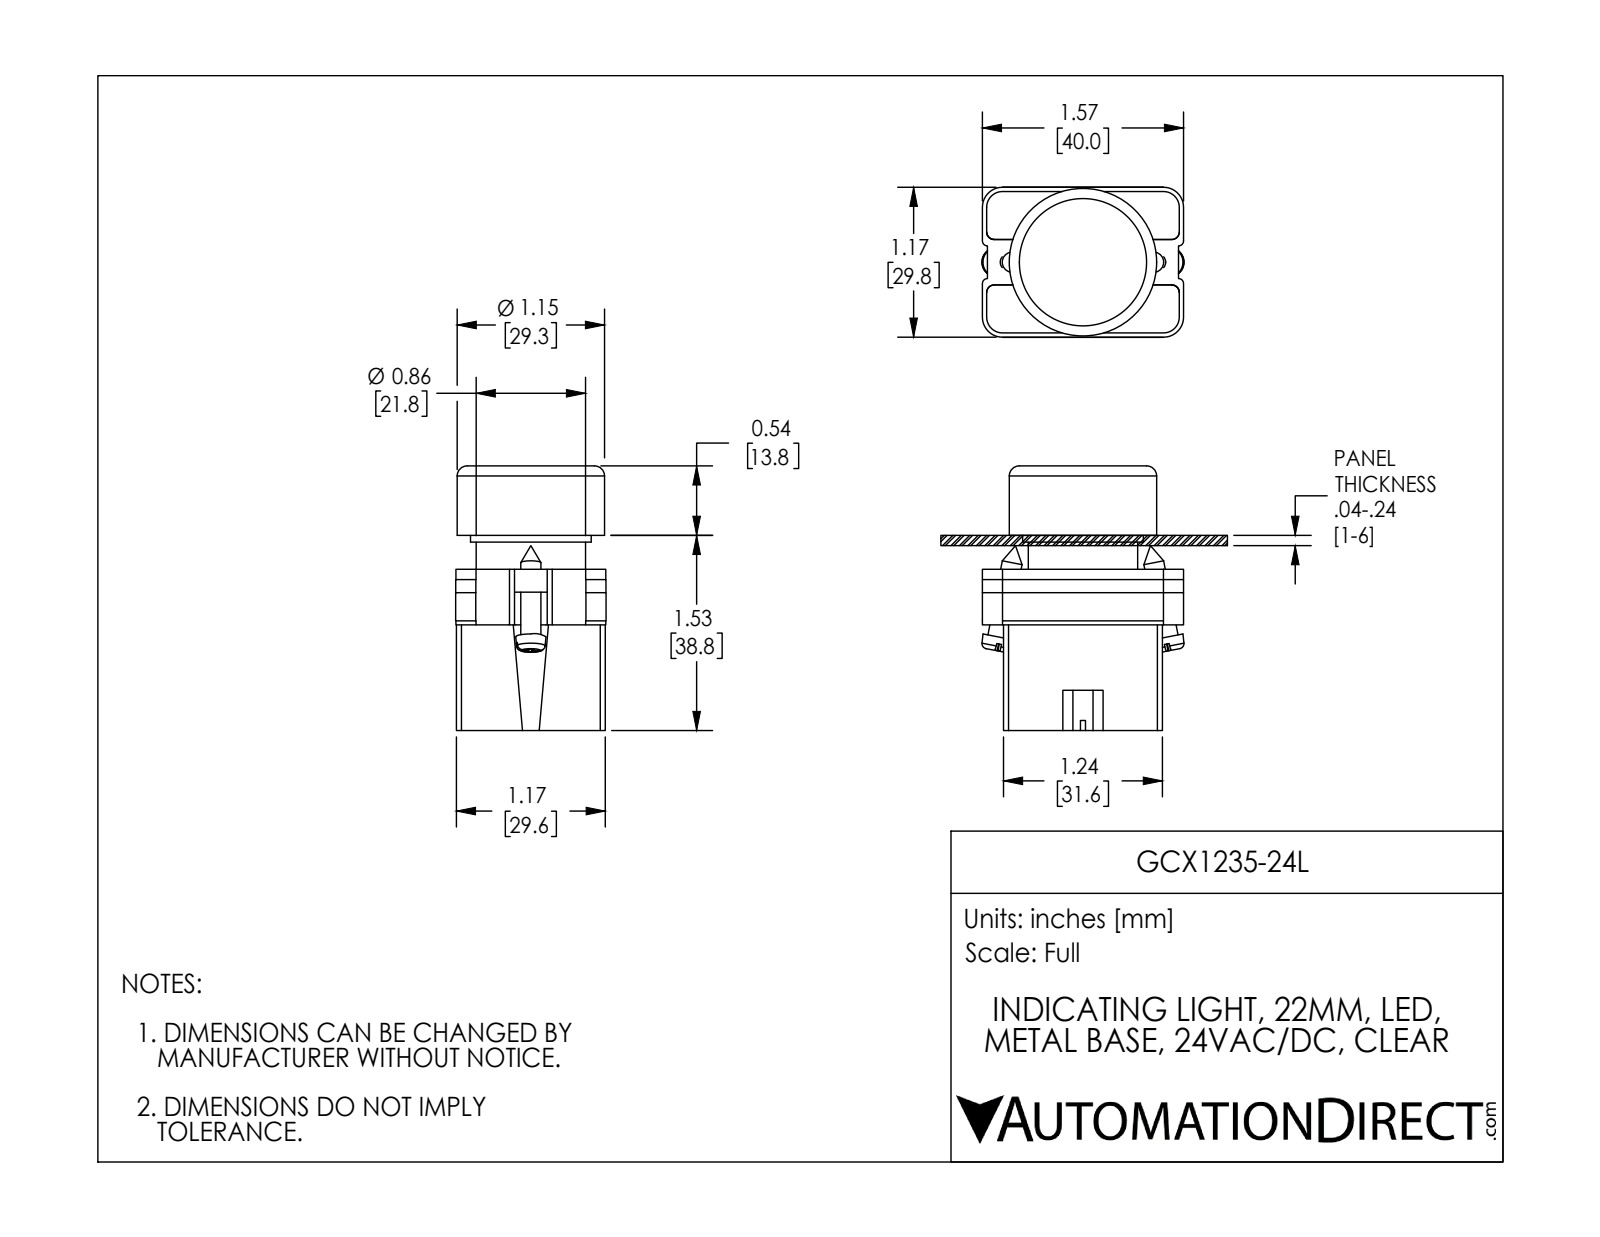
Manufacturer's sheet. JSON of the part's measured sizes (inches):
{"part_name": "GCX1235-24L; ecx1029; GCX1235L OPERATOR; ECX1050", "step_written_by": "SolidWorks 2016 (AUTOMOTIVE_DESIGN)", "units": "inches", "bodies": {"solids": 7, "faces": 339, "planar": 178, "cylindrical": 134, "other": 27}, "overall_size": [2.071, 1.581, 1.177], "volume_in3": 2.268, "surface_area_in2": 31.19, "round_holes": [[0.124, 2], [0.13, 2], [0.197, 1], [0.469, 1], [0.852, 1], [0.878, 1], [0.888, 1], [1.102, 1]], "round_bosses_or_shafts": [[0.157, 4], [1.154, 1], [1.092, 1], [0.945, 1], [0.856, 1], [0.78, 1], [0.504, 1]], "partial_cylinders_radius": [[0.059, 24], [0.041, 12], [0.124, 12], [0.157, 12], [0.039, 8], [0.128, 2], [0.392, 1], [0.398, 1]], "face_to_face_distances": [0.86, 1.244, 0.827, 1.687, 1.136, 0.033, 1.963, 0.276, 0.031, 1.165]}
